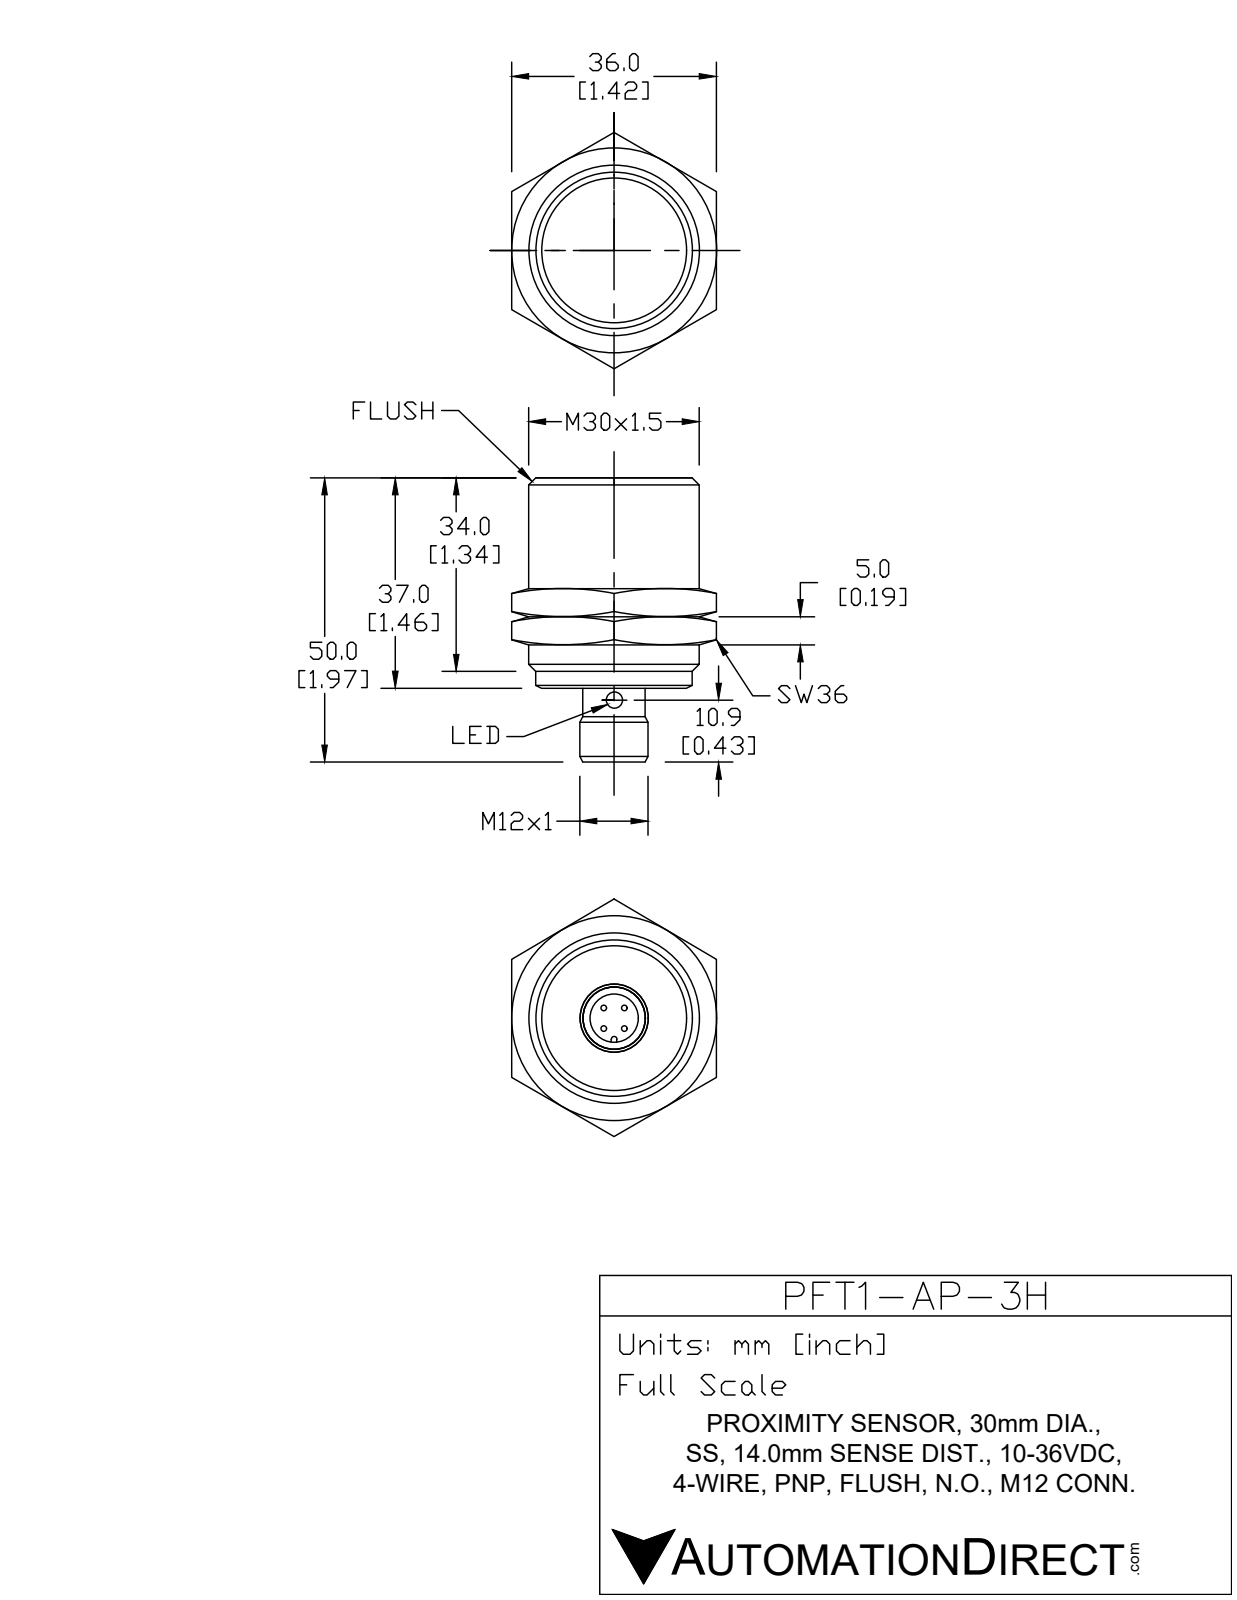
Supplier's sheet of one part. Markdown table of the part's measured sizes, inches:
| quantity | value |
| --- | --- |
| part name | PFT1-AP-3H |
| STEP written by | SolidWorks 2017 (AUTOMOTIVE_DESIGN) |
| units | inches |
| bodies | 3 solids, 93 faces (25 planar, 28 cylindrical, 40 other) |
| overall size | 1.969 × 1.637 × 1.417 |
| volume | 1.906 in³ |
| surface area | 14.46 in² |
| round holes (diameter × count) | 0.079 × 2, 0.354 × 1, 1.117 × 1 |
| round bosses / shafts (diameter × count) | 1.181 × 1, 1.102 × 1, 0.472 × 1, 0.394 × 1 |
| partial cylindrical surfaces (radius × count) | 0.02 × 1, 0.157 × 1 |
| main face-to-face distances | 0.197, 0.394, 1.417, 1.063, 1.457, 1.26, 0.866, 0.591, 1.102, 1.299 |
